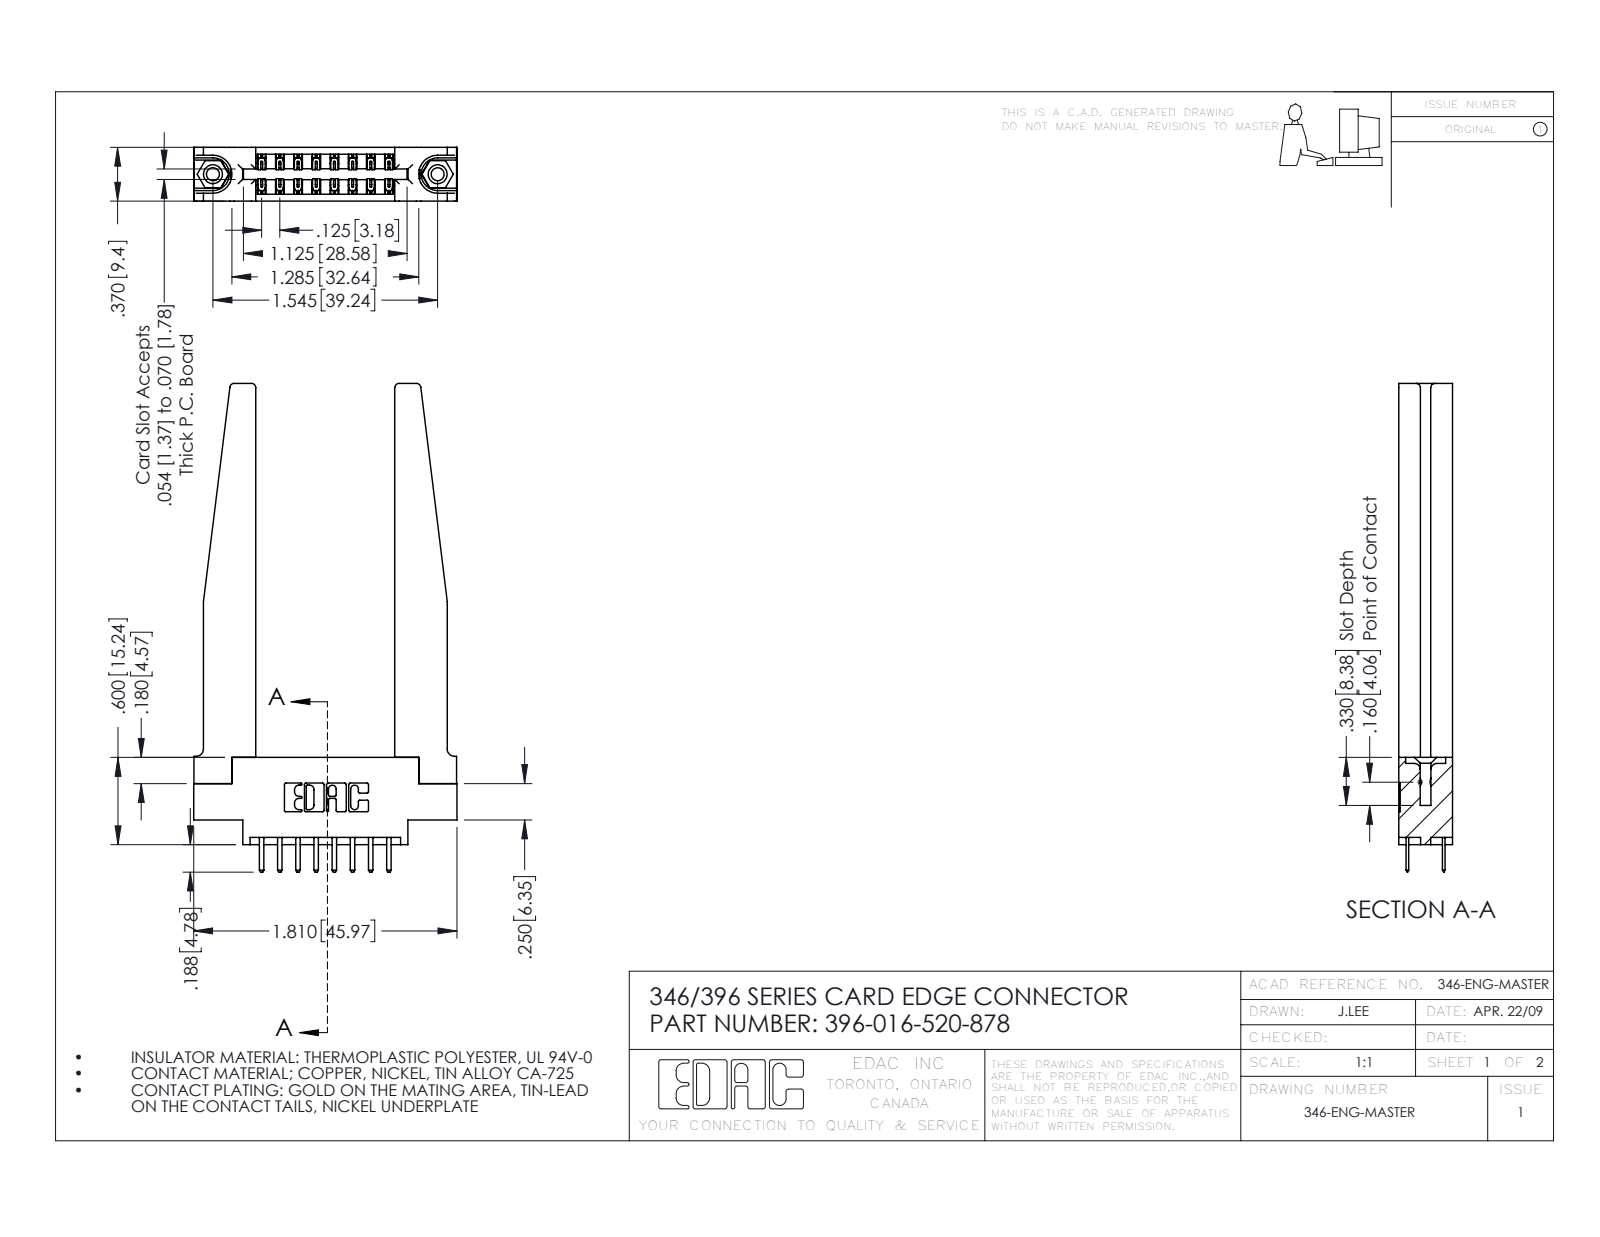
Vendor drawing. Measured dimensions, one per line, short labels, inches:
name: 346 Part_0.170 Offset - 0.156 Dia-TH; 396-016-520-878; 345-250-001_345-250-001-102; 346-220-078_345-220-078 (+1 more)
written by: SolidWorks 2016 (CONFIG_CONTROL_DESIGN)
unit: in
bodies: 21 solids, 1256 faces (814 planar, 390 cylindrical, 52 other)
size: 3.358 × 1.81 × 0.37
volume: 0.669 in³; area: 18.2 in²
holes: 2× ⌀0.089, 2× ⌀0.125, 2× ⌀0.156, 1× ⌀0.064
bosses: 2× ⌀0.155
rounds: 24× R0.006, 22× R0.01, 20× R0.01, 8× R0.03, 6× R0.007, 6× R0.031, 3× R0.026, 2× R0.014
face distances: 0.37, 0.15, 0.22, 0.25, 0.072, 0.148, 0.102, 0.048, 0.322, 0.173
hole spacings: 0.246, 1.341, 1.545
